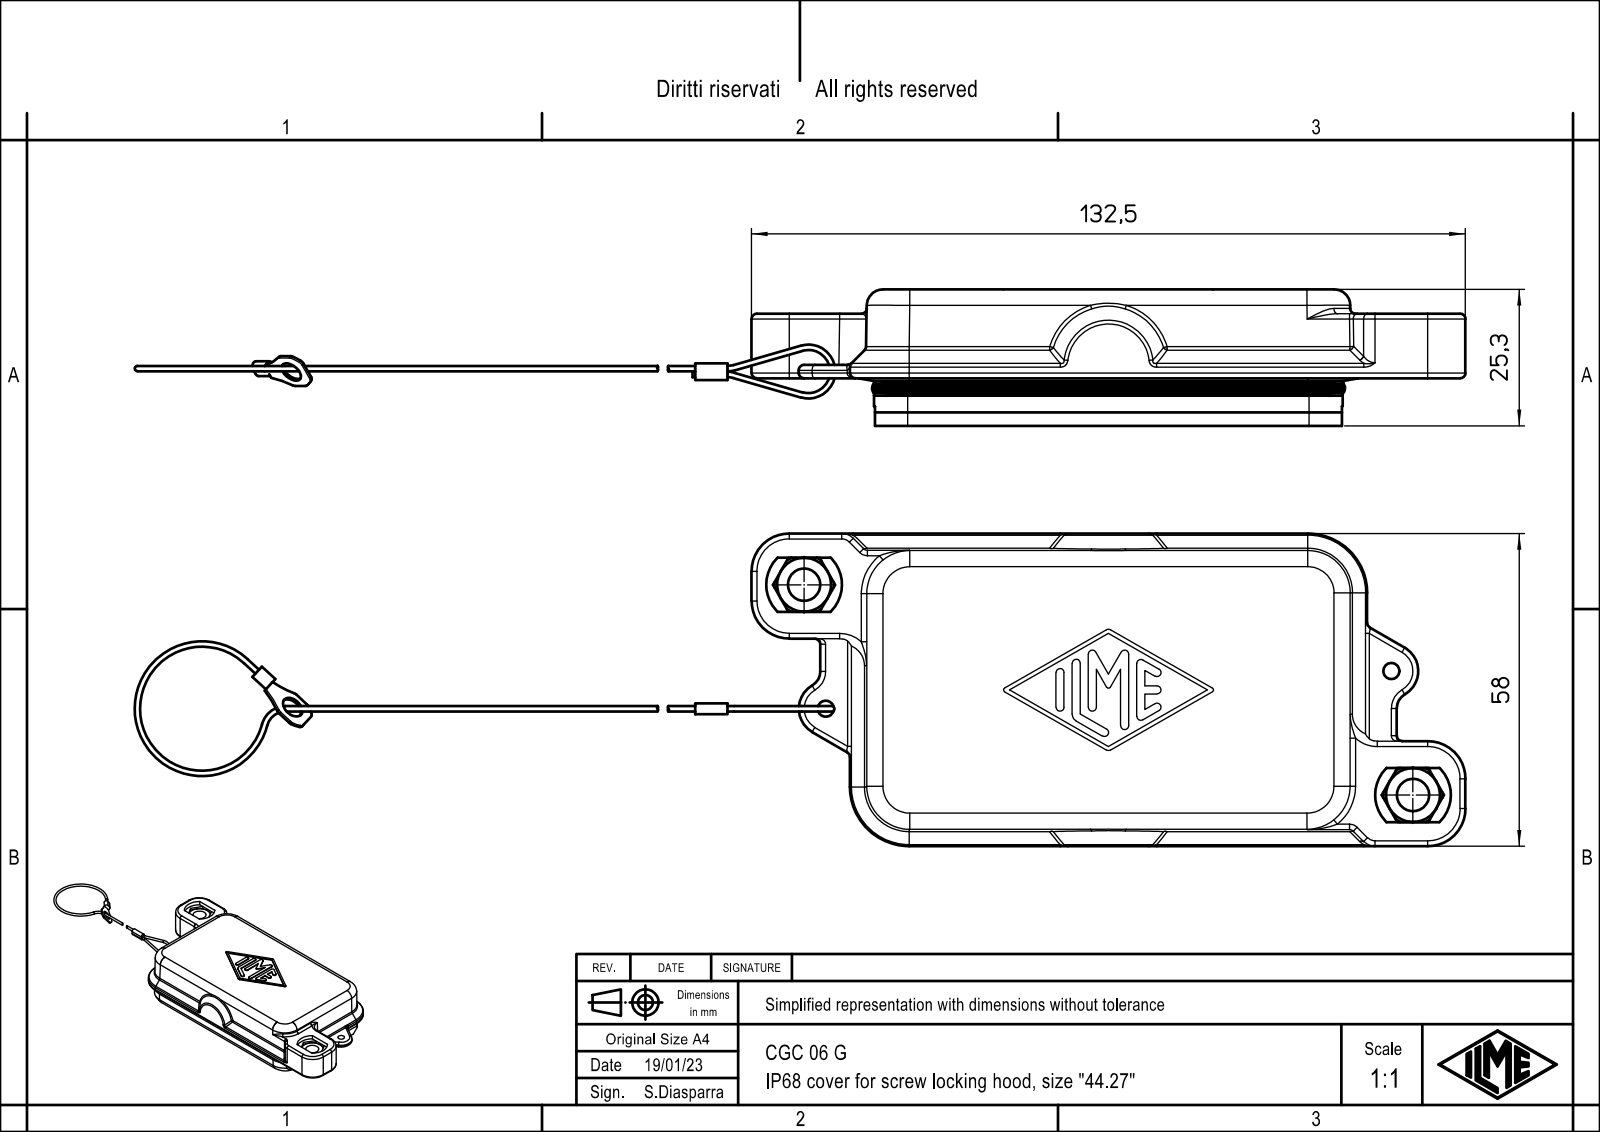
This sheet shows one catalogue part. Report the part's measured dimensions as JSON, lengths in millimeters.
{"part_name": "CGC 06 G", "step_written_by": "Creo Elements/Direct Modeling 20.1B 02-Apr-2019 (C) Parametric Technology GmbH (AUTOMOTIVE_DESIGN)", "units": "millimeters", "bodies": {"solids": 1, "faces": 455, "planar": 150, "cylindrical": 157, "other": 148}, "overall_size": [362.54, 58, 25.6], "volume_mm3": 46804, "surface_area_mm2": 27079, "round_holes": [[3, 2], [6, 2], [4.2, 1]], "round_bosses_or_shafts": [[1, 5]], "partial_cylinders_radius": [[1, 53], [0.75, 15], [3, 8], [6.5, 8], [8, 7], [5, 6], [1.4, 4], [2, 4]], "face_to_face_distances": [3, 16.5, 13.5, 8.8, 22.3, 25.3, 55, 1.5, 4.5, 12], "hole_center_spacings": [23.35, 110.17, 105.23, 119.54]}
